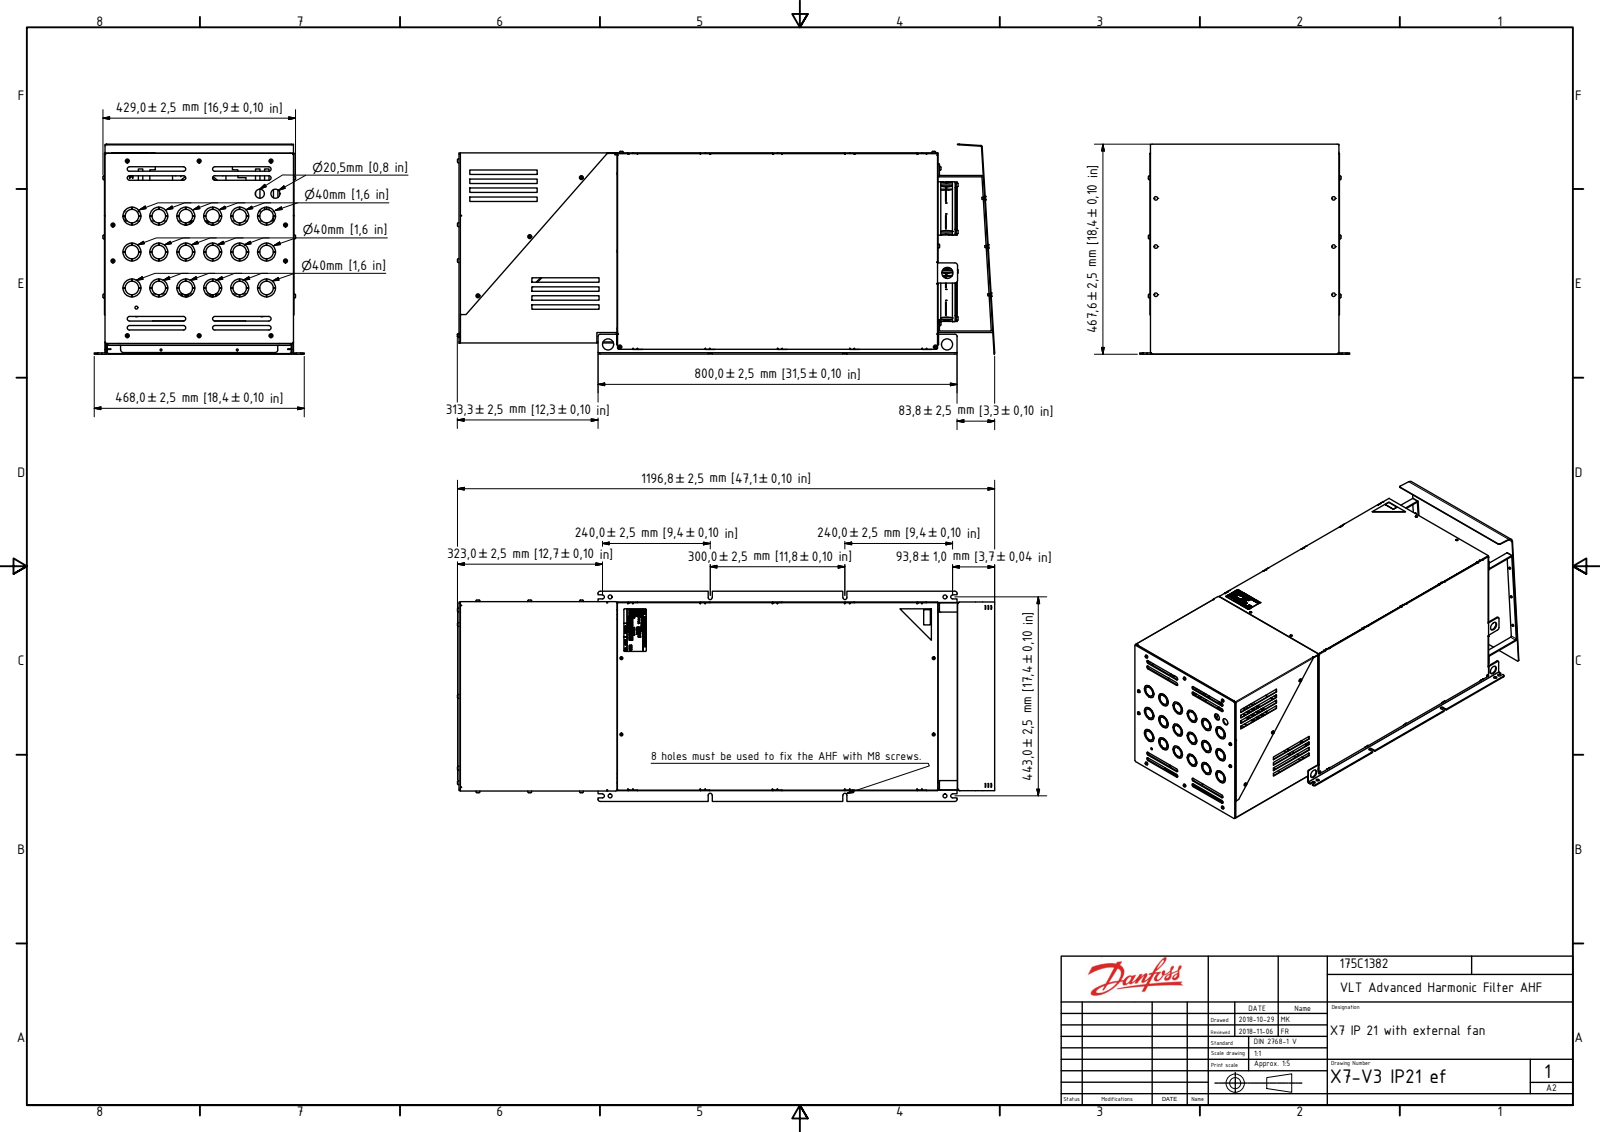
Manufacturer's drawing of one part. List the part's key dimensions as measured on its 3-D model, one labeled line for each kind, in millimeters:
Part name (STEP PRODUCT): X7.3 IP21 ef
STEP written by: Autodesk Inventor 2018 (AUTOMOTIVE_DESIGN)
Units: millimetres
Bodies: 86 solids, 13844 faces (8304 planar, 3977 cylindrical, 1563 other)
Overall size (bounding box): 1197.13 × 468 × 467.63
Volume: 4 458 000 mm³ · Surface area: 7 116 000 mm²
Round holes (diameter × count): ⌀5.5 ×60, ⌀4.13 ×32, ⌀3.24 ×21, ⌀4.5 ×19, ⌀40 ×18, ⌀7 ×17, ⌀5 ×13, ⌀4.3 ×12, ⌀6.5 ×12, ⌀9 ×10, ⌀2.46 ×8, ⌀2.73 ×8
Round bosses / shafts (diameter × count): ⌀1.5 ×48, ⌀8.5 ×35, ⌀5 ×26, ⌀16 ×20, ⌀8 ×14, ⌀4.5 ×14, ⌀4 ×14, ⌀30 ×12
Partial cylindrical surfaces — rounded edges, fillets, slot ends (radius × count): R2 ×565, R0.3 ×222, R1.15 ×198, R0.31 ×132, R0.5 ×79, R1 ×68, R5 ×67, R0.31 ×66
Main face-to-face distances: 1, 3, 419, 2, 420, 418, 253, 417, 421, 1.5
Hole centre spacings: 100, 200, 80, 144.22, 60, 120, 173, 196.98
